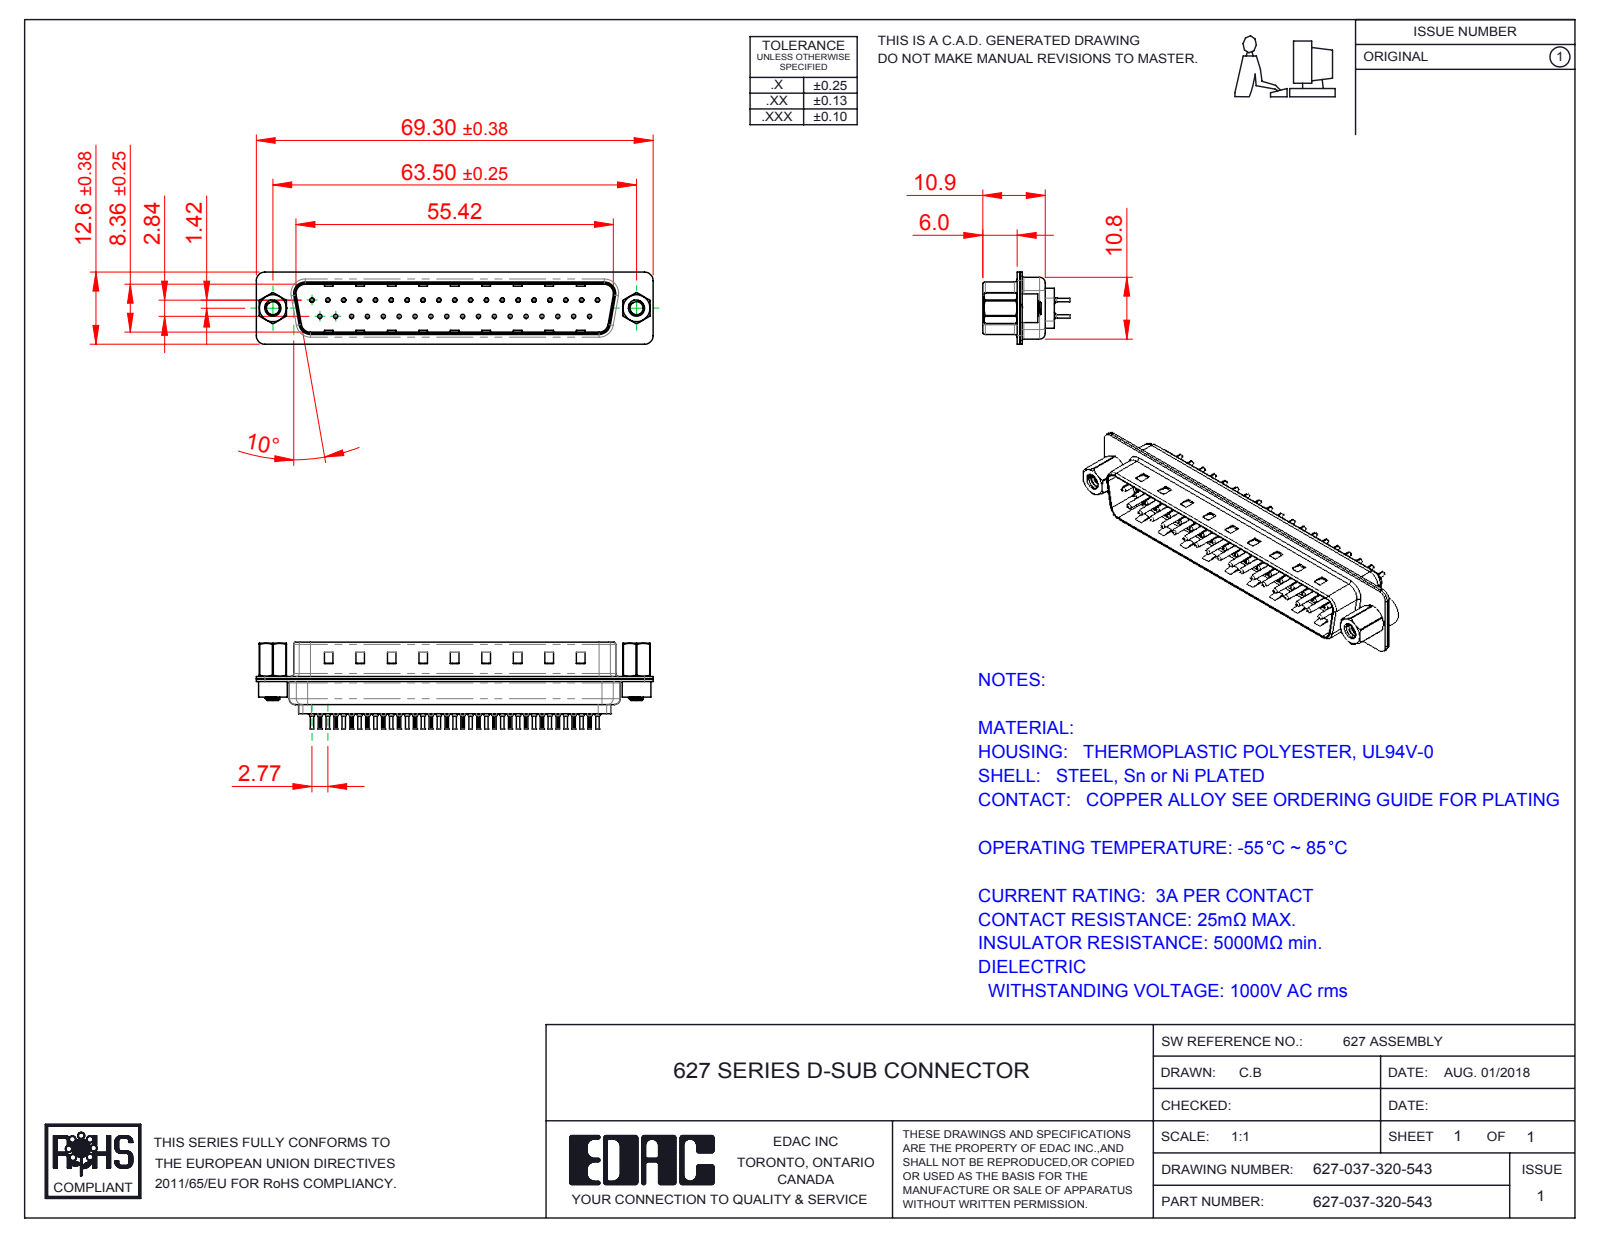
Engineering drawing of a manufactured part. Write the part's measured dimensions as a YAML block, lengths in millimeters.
part_name: "627 Housing_37 LP; 627 Contact Row 1_20L; 627 Contact Row 2_20L; 627 4-40 Threaded Rivet (+4 more)"
step_written_by: "SolidWorks 2016 (CONFIG_CONTROL_DESIGN)"
units: millimeters
bodies: {solids: 44, faces: 4164, planar: 1113, cylindrical: 1582, other: 1469}
overall_size: [69.3, 15.2, 12.6]
volume: 3897
surface_area: 10946
round_holes:
  - {diameter: 0.2, count: 37}
  - {diameter: 0.35, count: 37}
  - {diameter: 1.1, count: 37}
  - {diameter: 1.6, count: 37}
  - {diameter: 2.26, count: 2}
  - {diameter: 2.29, count: 2}
  - {diameter: 4, count: 2}
  - {diameter: 4.8, count: 2}
round_bosses_or_shafts:
  - {diameter: 2, count: 37}
  - {diameter: 1.5, count: 37}
  - {diameter: 0.75, count: 37}
  - {diameter: 0.6, count: 37}
  - {diameter: 5, count: 2}
  - {diameter: 4.9, count: 2}
  - {diameter: 2.79, count: 2}
partial_cylinders:
  - {radius: 0.1, count: 74}
  - {radius: 1.5, count: 16}
  - {radius: 2, count: 12}
  - {radius: 0.5, count: 8}
  - {radius: 1.6, count: 8}
  - {radius: 0.25, count: 4}
  - {radius: 0.6, count: 4}
  - {radius: 0.65, count: 4}
face_to_face_distances: [0.4, 0.82, 9.58, 0.45, 8.76, 0.9, 1.5, 1.4, 6.05, 6.5]
hole_center_spacings: [3.16, 2.77, 5.54, 8.31, 5.04, 10.1, 11.08, 12.78]
